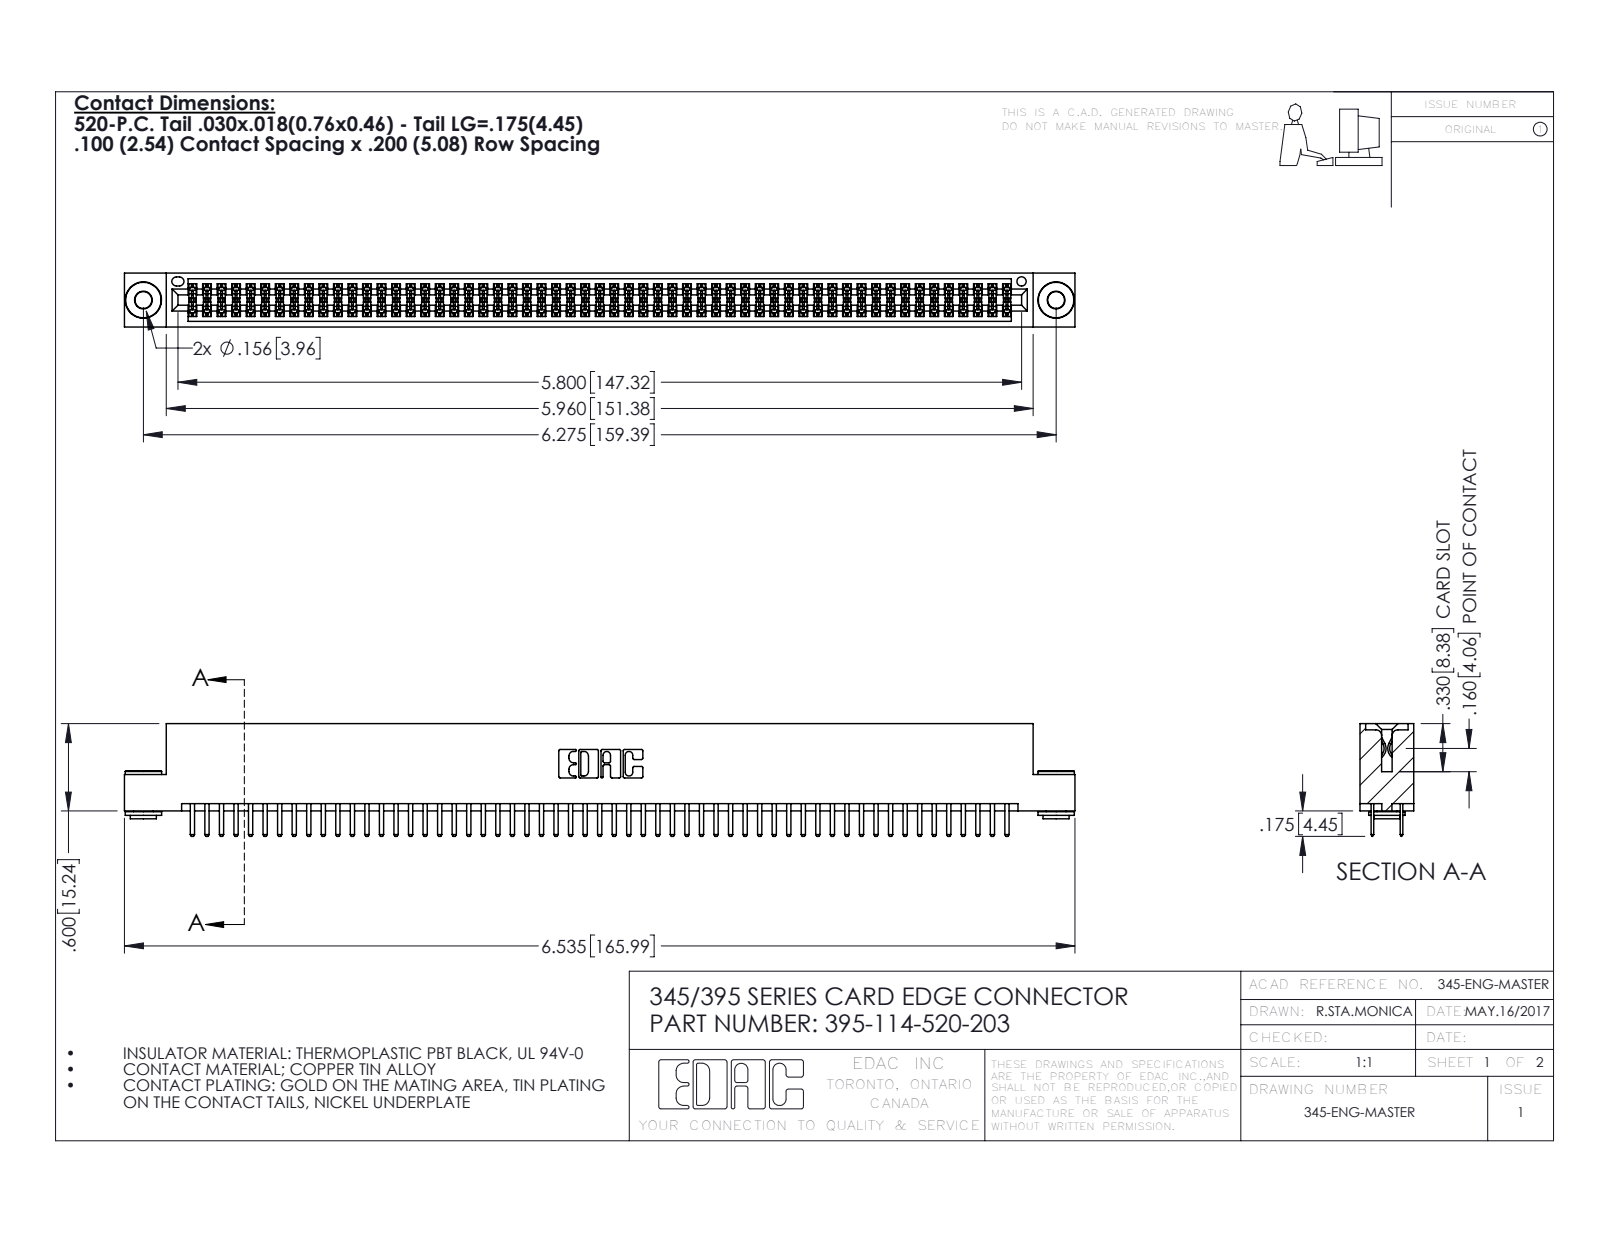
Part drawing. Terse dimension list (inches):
name: 395-114-520-203; 345 Part_Flush Mounting Lugs - 0.156 Dia-TH; 345-250-002_345-250-002-102; 345-292-001_345-293-120
written by: SolidWorks 2016 (CONFIG_CONTROL_DESIGN)
unit: in
bodies: 117 solids, 6320 faces (4080 planar, 2232 cylindrical, 8 other)
size: 6.535 × 0.775 × 0.37
volume: 0.991 in³; area: 37.79 in²
holes: 2× ⌀0.116, 2× ⌀0.156, 1× ⌀0.064
bosses: 2× ⌀0.25, 2× ⌀0.18, 2× ⌀0.136
rounds: 171× R0.006, 118× R0.01, 22× R0.01, 6× R0.007, 6× R0.031, 3× R0.026, 2× R0.014, 2× R0.019
face distances: 0.072, 0.298, 0.2, 0.37, 0.025, 0.098, 0.272, 0.225, 0.022, 0.072
hole spacings: 0.27, 6.039, 6.275
